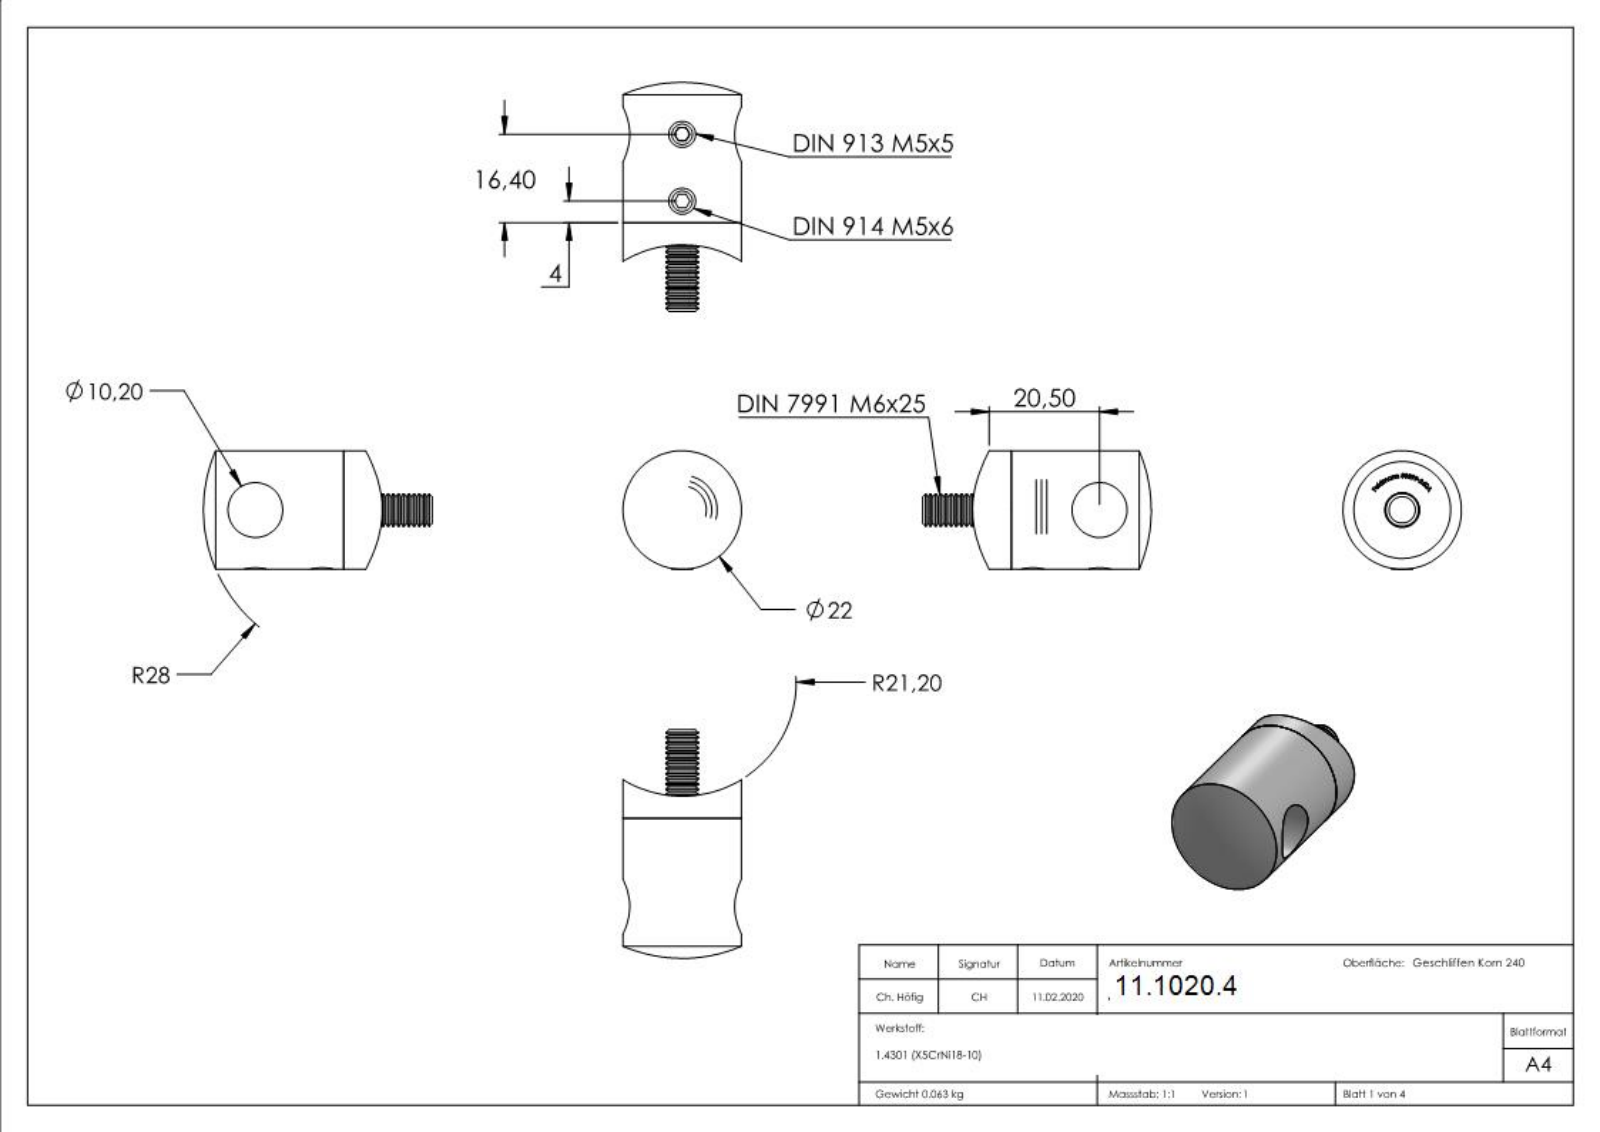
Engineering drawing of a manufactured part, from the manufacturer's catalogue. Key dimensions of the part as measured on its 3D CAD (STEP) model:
Part name (STEP PRODUCT): 50399-240A; Querstabhalter Teil2 Konfig_50XXX-240A Teil2 42,4; Querstabhalter Teil1 Konfig; DIN914 (+7 more)
STEP written by: SolidWorks 2015 (CONFIG_CONTROL_DESIGN)
Units: millimetres
Bodies: 5 solids, 380 faces (174 planar, 36 cylindrical, 170 other)
Overall size (bounding box): 70 × 42.45 × 22
Volume: 8 682 mm³ · Surface area: 6 136 mm²
Round holes (diameter × count): ⌀4.2 ×2, ⌀6.5 ×1, ⌀10.2 ×1, ⌀12 ×1, ⌀18 ×1
Round bosses / shafts (diameter × count): ⌀5 ×2, ⌀22 ×1, ⌀11.9 ×1, ⌀11.57 ×1, ⌀6 ×1
Partial cylindrical surfaces — rounded edges, fillets, slot ends (radius × count): R21.2 ×1
Main face-to-face distances: 2.1, 10.65, 8.55, 2.5, 9.6, 7.5, 1.05, 14.35, 16.45, 23.95
Hole centre spacings: 12.4
